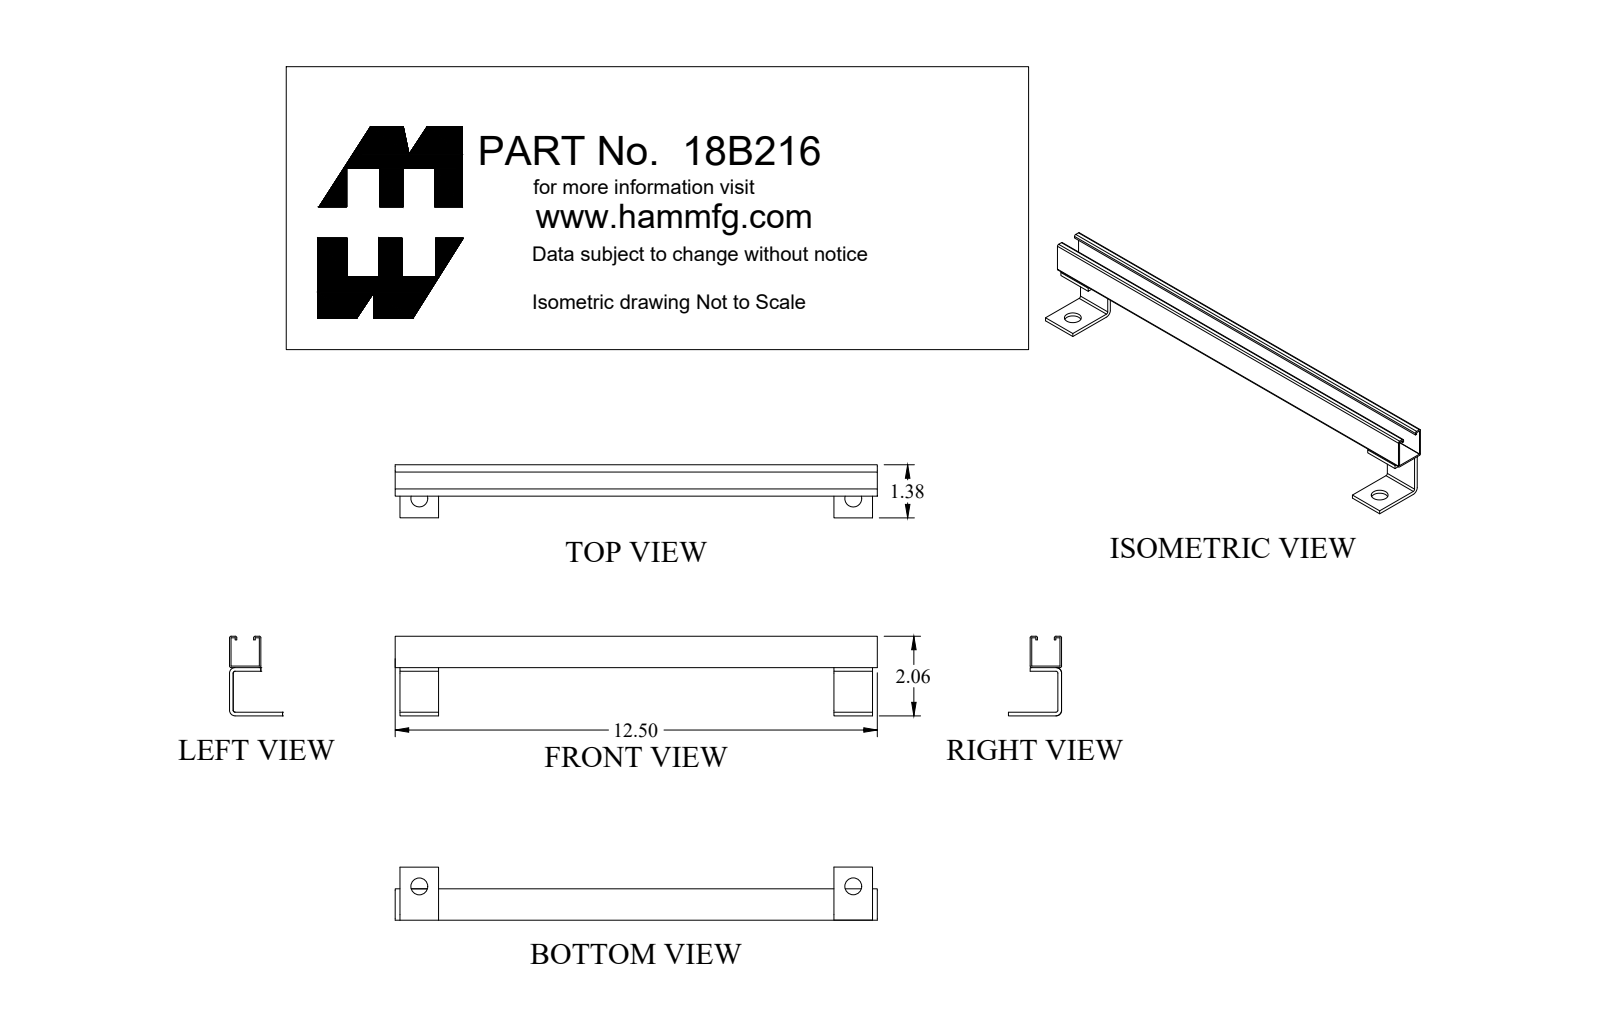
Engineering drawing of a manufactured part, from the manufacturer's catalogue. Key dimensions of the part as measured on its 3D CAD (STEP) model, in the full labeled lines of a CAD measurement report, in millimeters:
Part name (STEP PRODUCT): 18B216
STEP written by: SolidWorks 2018 (AUTOMOTIVE_DESIGN)
Units: millimetres
Bodies: 3 solids, 60 faces (38 planar, 22 cylindrical, 0 other)
Overall size (bounding box): 317.5 × 52.4 × 35
Volume: 31 550 mm³ · Surface area: 53 360 mm²
Round holes (diameter × count): ⌀11.1 ×2
Partial cylindrical surfaces — rounded edges, fillets, slot ends (radius × count): R1.1 ×6, R1.2 ×4, R3.6 ×4
Main face-to-face distances: 1, 19.6, 20.7, 18.6, 19.6, 2.4, 29.3, 20.7, 18.6, 3.8
Hole centre spacings: 285.8
